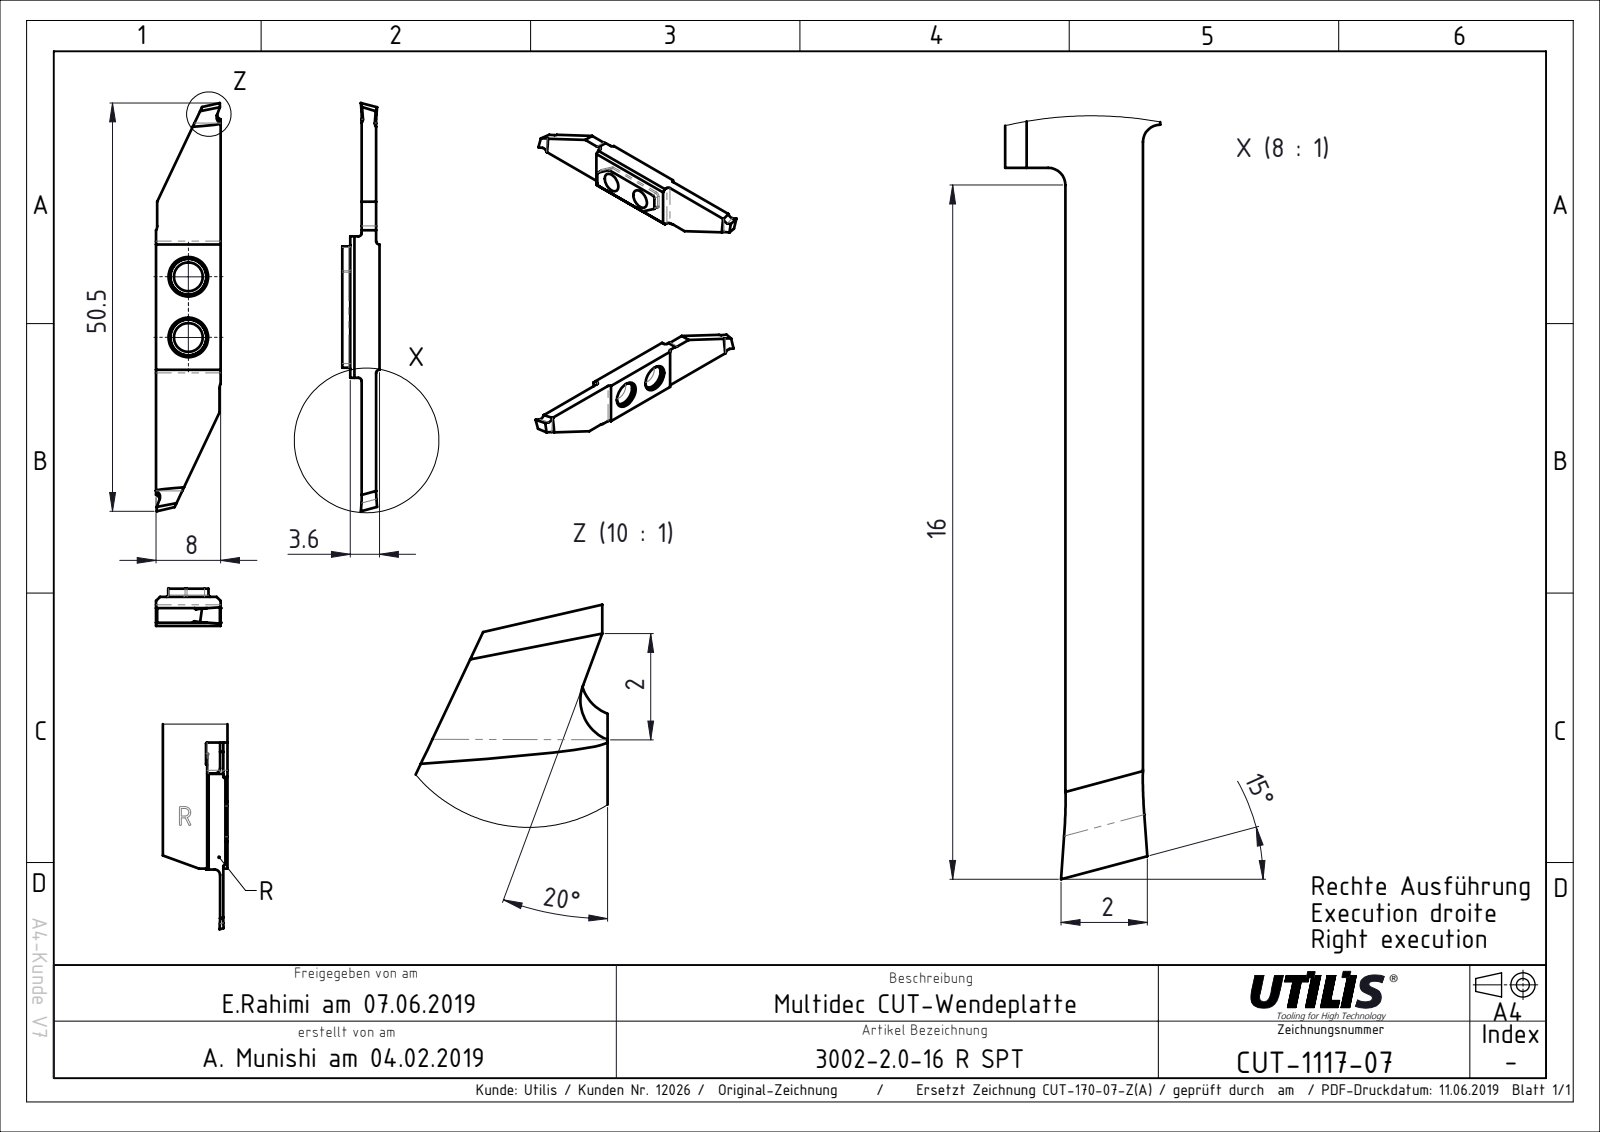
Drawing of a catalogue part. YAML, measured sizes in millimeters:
part_name: "CUT-1117; ASME Y14.5"
step_written_by: "FormatWorks Professional (AP242_MANAGED_MODEL_BASED_3D_ENGINEERING_MIM_LF)"
units: millimeters
bodies: {solids: 1, faces: 34, planar: 24, cylindrical: 10, other: 0}
overall_size: [50.5, 8, 3.6]
volume: 759
surface_area: 964
round_holes:
  - {diameter: 3.55, count: 2}
partial_cylinders:
  - {radius: 0.4, count: 4}
  - {radius: 1, count: 2}
face_to_face_distances: [1.78, 2.19, 0.41, 1.41, 3.19, 3.6, 8, 18.09, 7.85, 17.5]
hole_center_spacings: [7.5]
